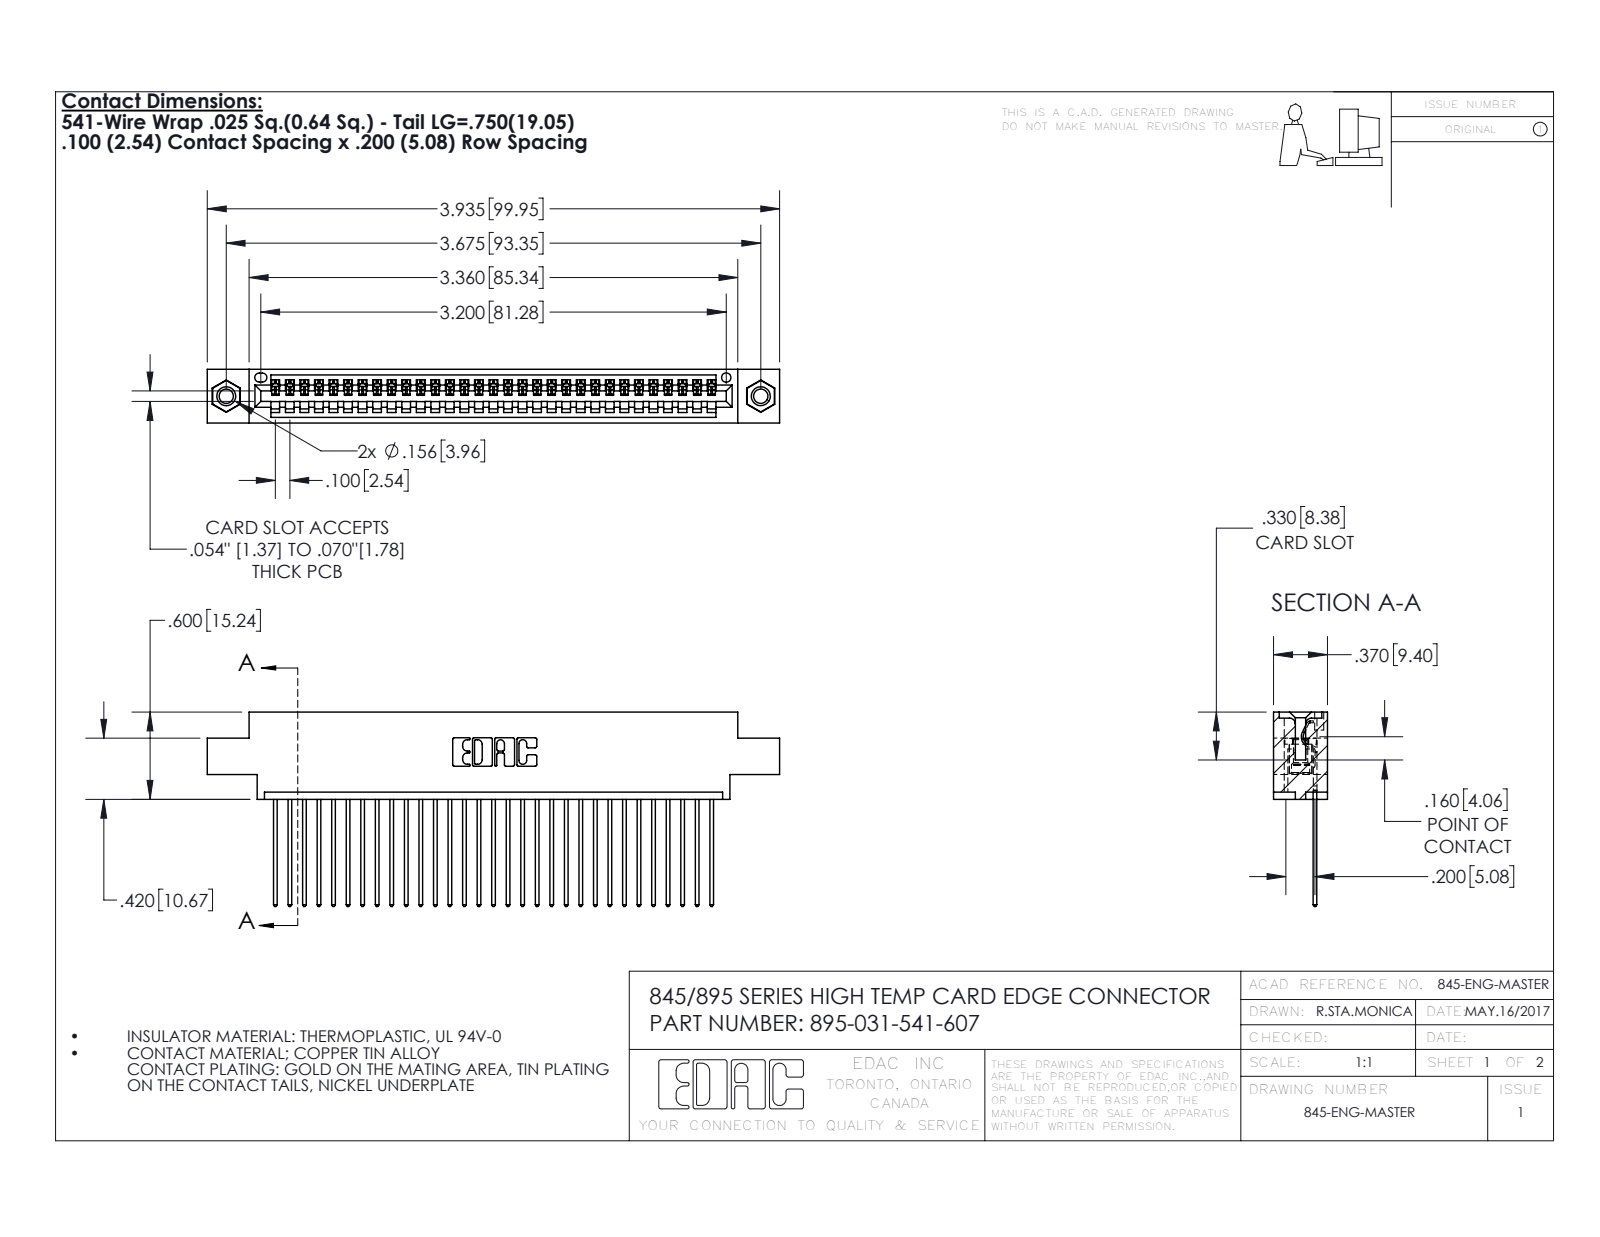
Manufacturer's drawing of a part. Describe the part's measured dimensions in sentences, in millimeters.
The part is named "345-250-001_345-250-005-103; 345-292-001_345-293-141; 345 Part_0.170 Offset - 0.156 Dia-TI; 395-031-541-607". Its 3-D file was written by "SolidWorks 2016 (CONFIG_CONTROL_DESIGN)". It is 34 solids with 1988 faces: 1356 planar, 616 cylindrical and 16 other. Overall it measures 99.9 by 34 by 9.4 millimeters. Its volume is 9 370 cubic millimeters and its surface area 13 080 square millimeters. Round holes: 2 of diameter 2.5, 2 of diameter 3.2, 2 of diameter 4, 1 of diameter 1.6. Round bosses or shafts: 2 of diameter 3.9. Partial cylindrical surfaces (rounded edges, fillets, slot ends): 62 of radius 0.2, 62 of radius 0.3, 22 of radius 0.3, 6 of radius 0.2, 6 of radius 0.8, 3 of radius 0.7, 2 of radius 0.8, 2 of radius 1. The main face-to-face distances are 1.8, 7.6, 9.4, 2.5, 6.9, 0.6, 5.1, 5.7, 4.4, 3.8. The hole center spacings are 6.9, 87.4, 93.3.
